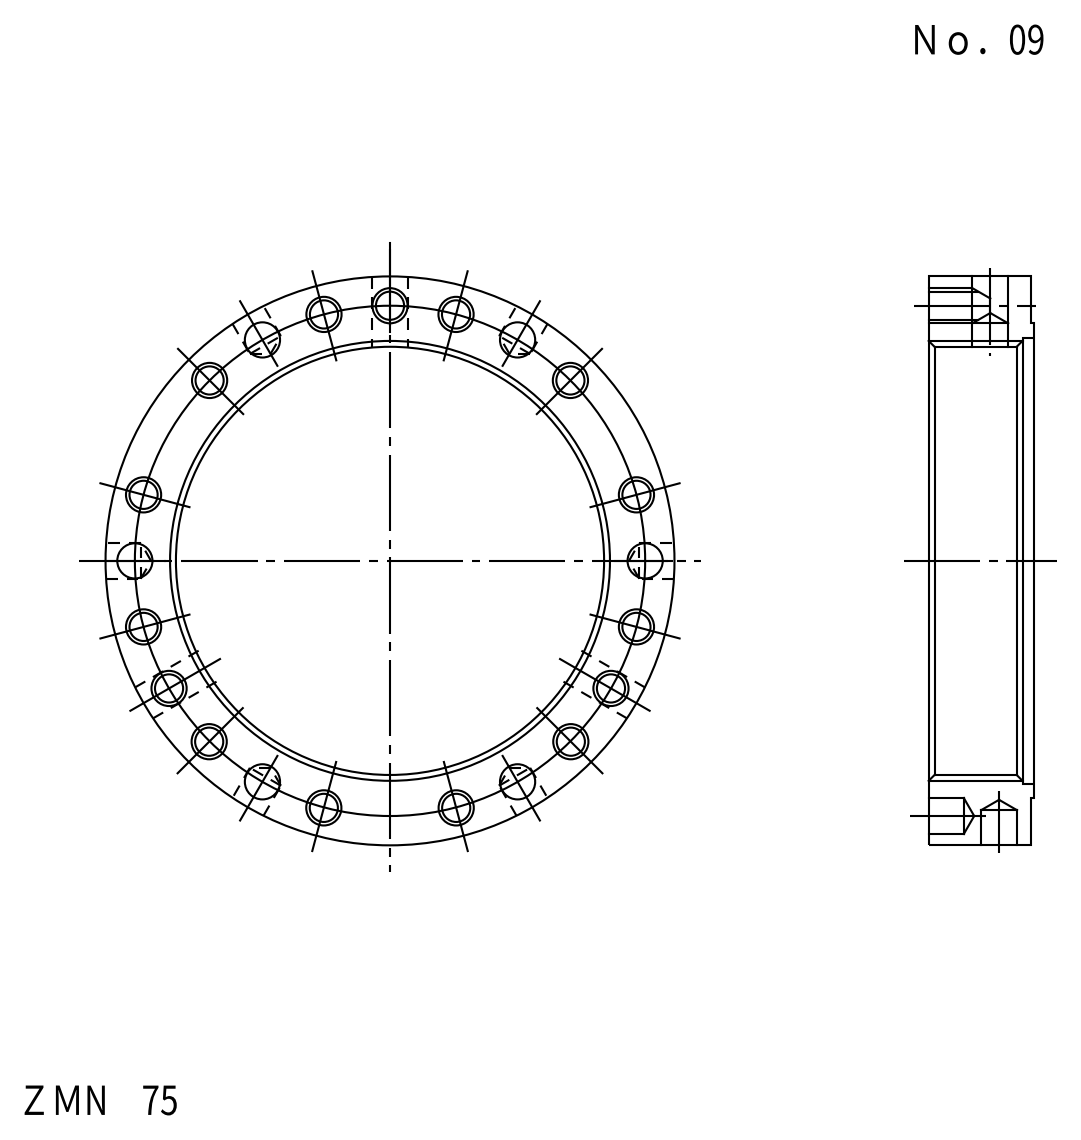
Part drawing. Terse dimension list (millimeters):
name: FKD ZMN75
written by: Autodesk Inventor LT (CONFIG_CONTROL_DESIGN)
unit: mm
bodies: 1 solid, 62 faces (4 planar, 34 cylindrical, 24 other)
size: 97 × 97 × 18
volume: 45 863 mm³; area: 19 869 mm²
holes: 14× ⌀4.92, 12× ⌀6.1, 1× ⌀4.92, 1× ⌀75, 1× ⌀76
bosses: 1× ⌀97, 1× ⌀81
face distances: 17.5, 0.5, 18, 1.5, 1, 16.5
hole spacings: 43.5, 52.96, 61.52, 69.02, 80.38, 86.26, 22.52, 11.36
